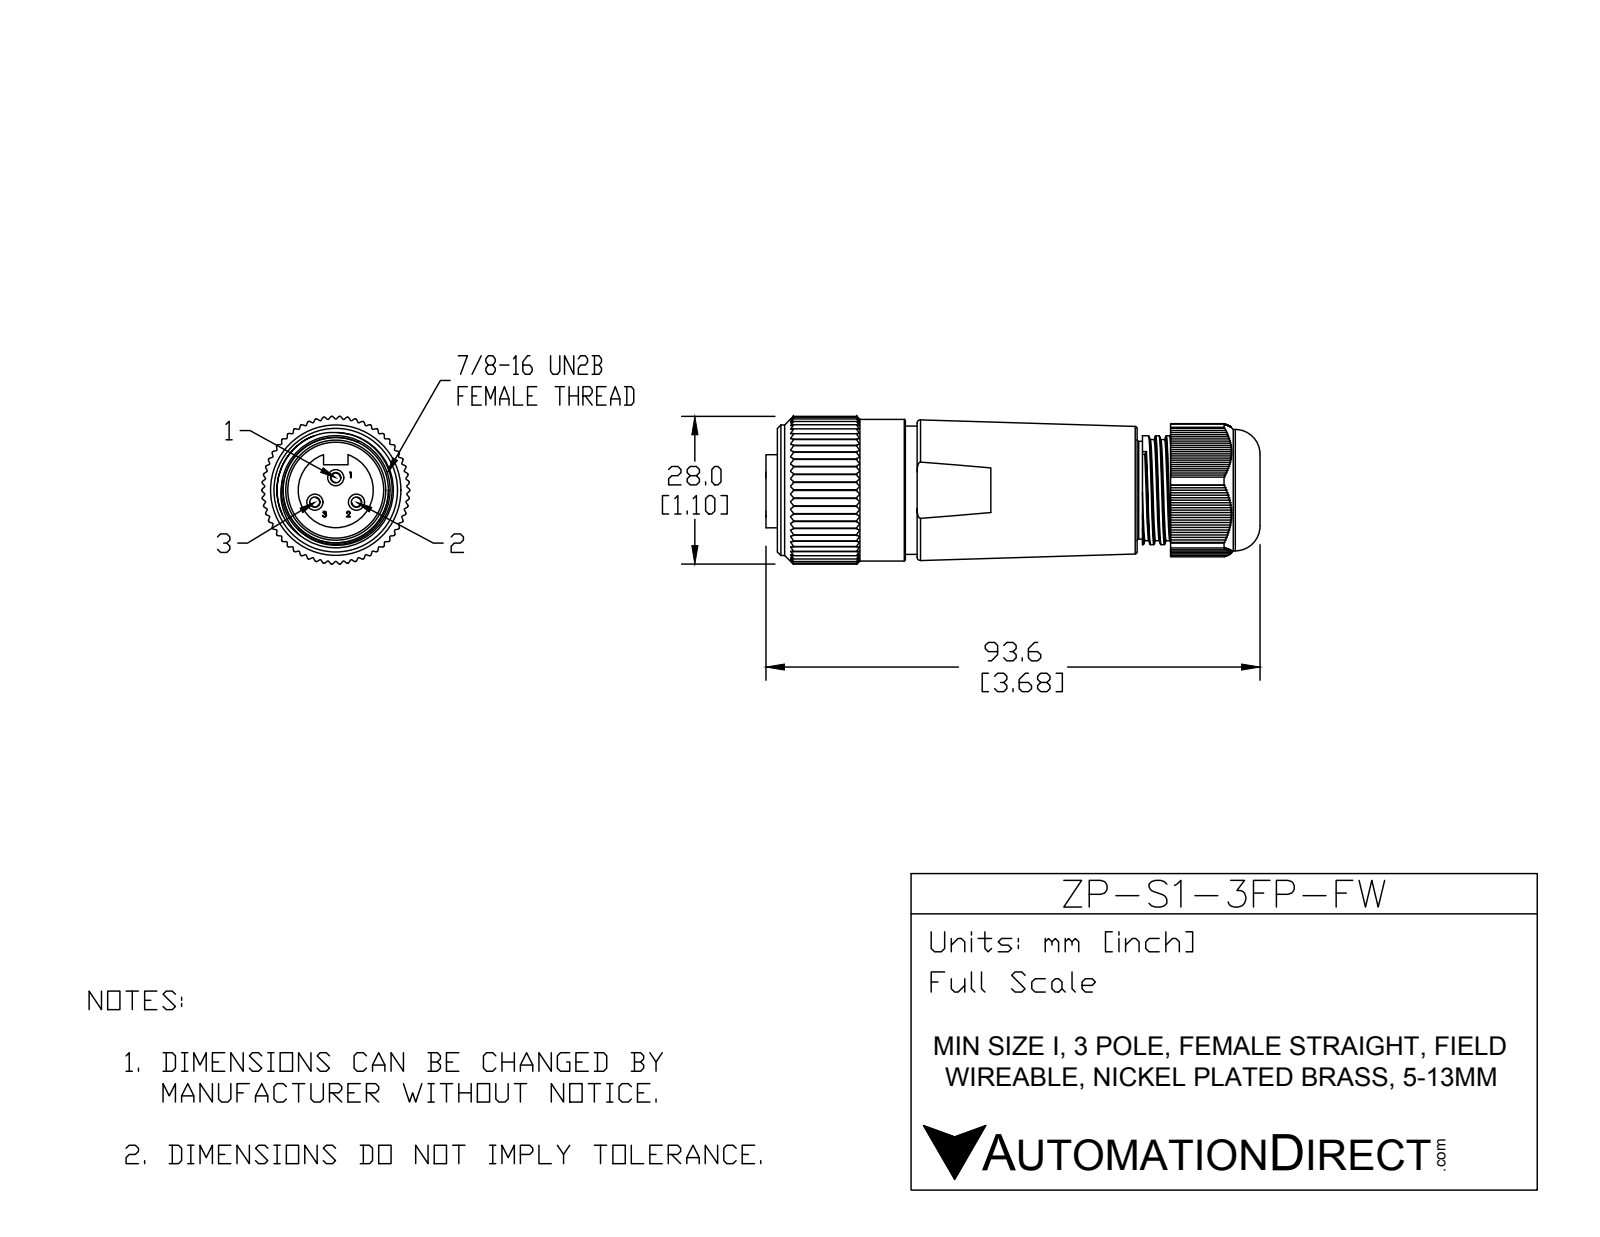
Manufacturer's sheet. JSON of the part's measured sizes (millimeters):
{"part_name": "MIN-3FP-FW", "step_written_by": "SolidWorks 2015 (AUTOMOTIVE_DESIGN)", "units": "millimeters", "bodies": {"solids": 1, "faces": 815, "planar": 445, "cylindrical": 316, "other": 54}, "overall_size": [93.62, 28, 27.96], "volume_mm3": 43860, "surface_area_mm2": 11973, "round_holes": [[3.05, 3], [3.5, 1], [13.46, 1], [20.57, 1], [25.4, 1]], "round_bosses_or_shafts": [[26.8, 1], [24.68, 1], [24.3, 1], [24.2, 1], [22.99, 1], [20.6, 1], [20, 1], [18.14, 1]], "partial_cylinders_radius": [[0.25, 116], [0.2, 58], [13.23, 1], [14, 1]], "face_to_face_distances": [0.36, 0.72, 1.08, 18.94, 1.44, 1.8, 15.39, 18.92, 24.4, 7.01], "hole_center_spacings": [4.54, 6.07, 2.36, 7.88]}
